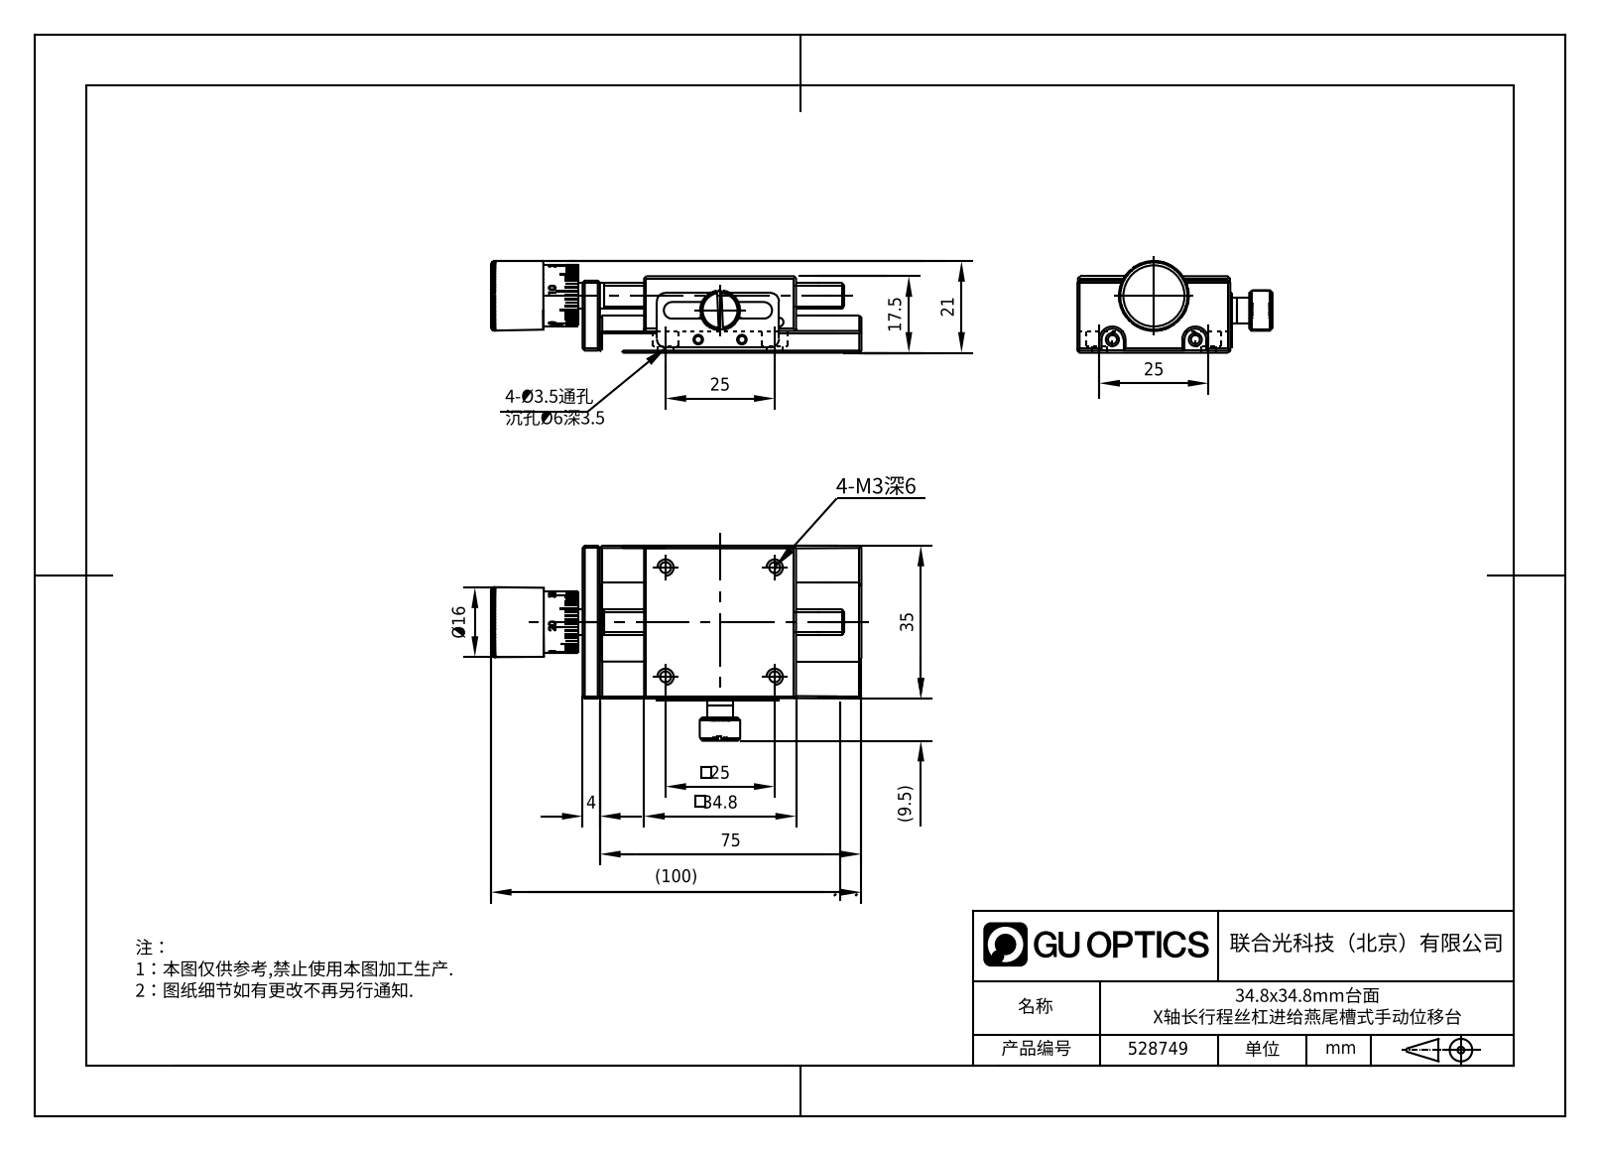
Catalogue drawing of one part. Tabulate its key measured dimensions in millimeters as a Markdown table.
| quantity | value |
| --- | --- |
| part name | 528749 |
| STEP written by | SolidWorks 2020 (CONFIG_CONTROL_DESIGN) |
| units | millimeters |
| bodies | 16 solids, 542 faces (258 planar, 144 cylindrical, 140 other) |
| overall size | 99 × 42.14 × 20.5 |
| volume | 35 395 mm³ |
| surface area | 20 973 mm² |
| round holes (diameter × count) | 1.6 × 6, 2.5 × 6, 2.05 × 5, 6 × 5, 3.4 × 4, 3 × 3, 1.5 × 2, 2.2 × 2, 3.5 × 1, 4.1 × 1, 5 × 1, 7 × 1 |
| round bosses / shafts (diameter × count) | 4.5 × 3, 4 × 3, 2 × 3, 2.5 × 2, 13 × 1, 8.5 × 1, 7 × 1, 6.5 × 1 |
| partial cylindrical surfaces (radius × count) | 0.3 × 8, 0.5 × 4, 2 × 4, 1.8 × 2, 2.5 × 2, 7.5 × 1 |
| main face-to-face distances | 5, 3.5, 8.5, 9, 12.5, 17.5, 34.9, 34.8, 3.8, 8.7 |
| hole center spacings | 25, 9, 3, 5.25, 13.77, 13.79, 18, 35.36 |
